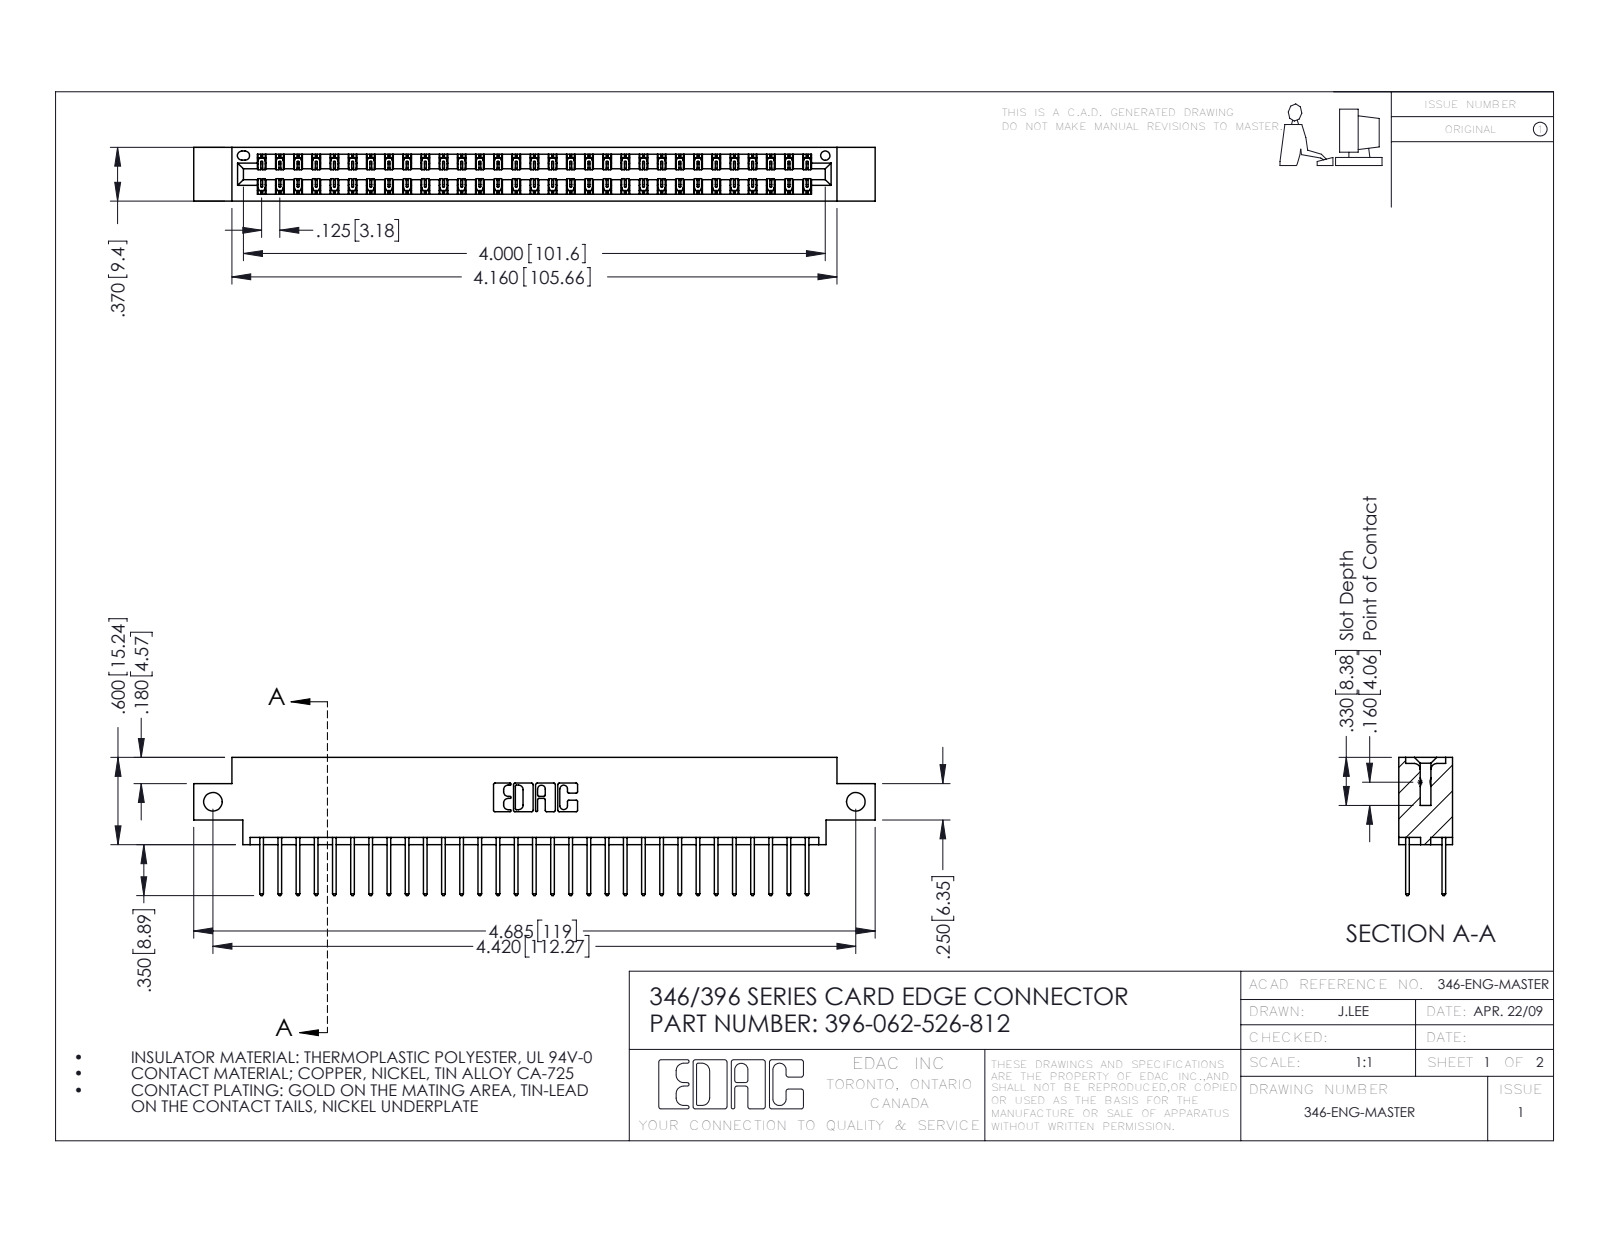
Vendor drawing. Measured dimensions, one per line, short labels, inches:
name: 396-062-526-812; 345-292-001_345-293-126; 346 Part_0.170 Offset - Side Mount
written by: SolidWorks 2016 (CONFIG_CONTROL_DESIGN)
unit: in
bodies: 63 solids, 3350 faces (2250 planar, 1100 cylindrical, 0 other)
size: 4.685 × 0.95 × 0.37
volume: 0.694 in³; area: 24.75 in²
holes: 2× ⌀0.128, 1× ⌀0.064
rounds: 93× R0.006, 62× R0.01, 22× R0.01, 6× R0.007, 6× R0.031, 3× R0.026, 2× R0.014, 2× R0.022
face distances: 0.048, 0.322, 0.25, 0.37, 0.072, 0.298, 0.025, 0.275, 0.148, 0.222
hole spacings: 4.42
